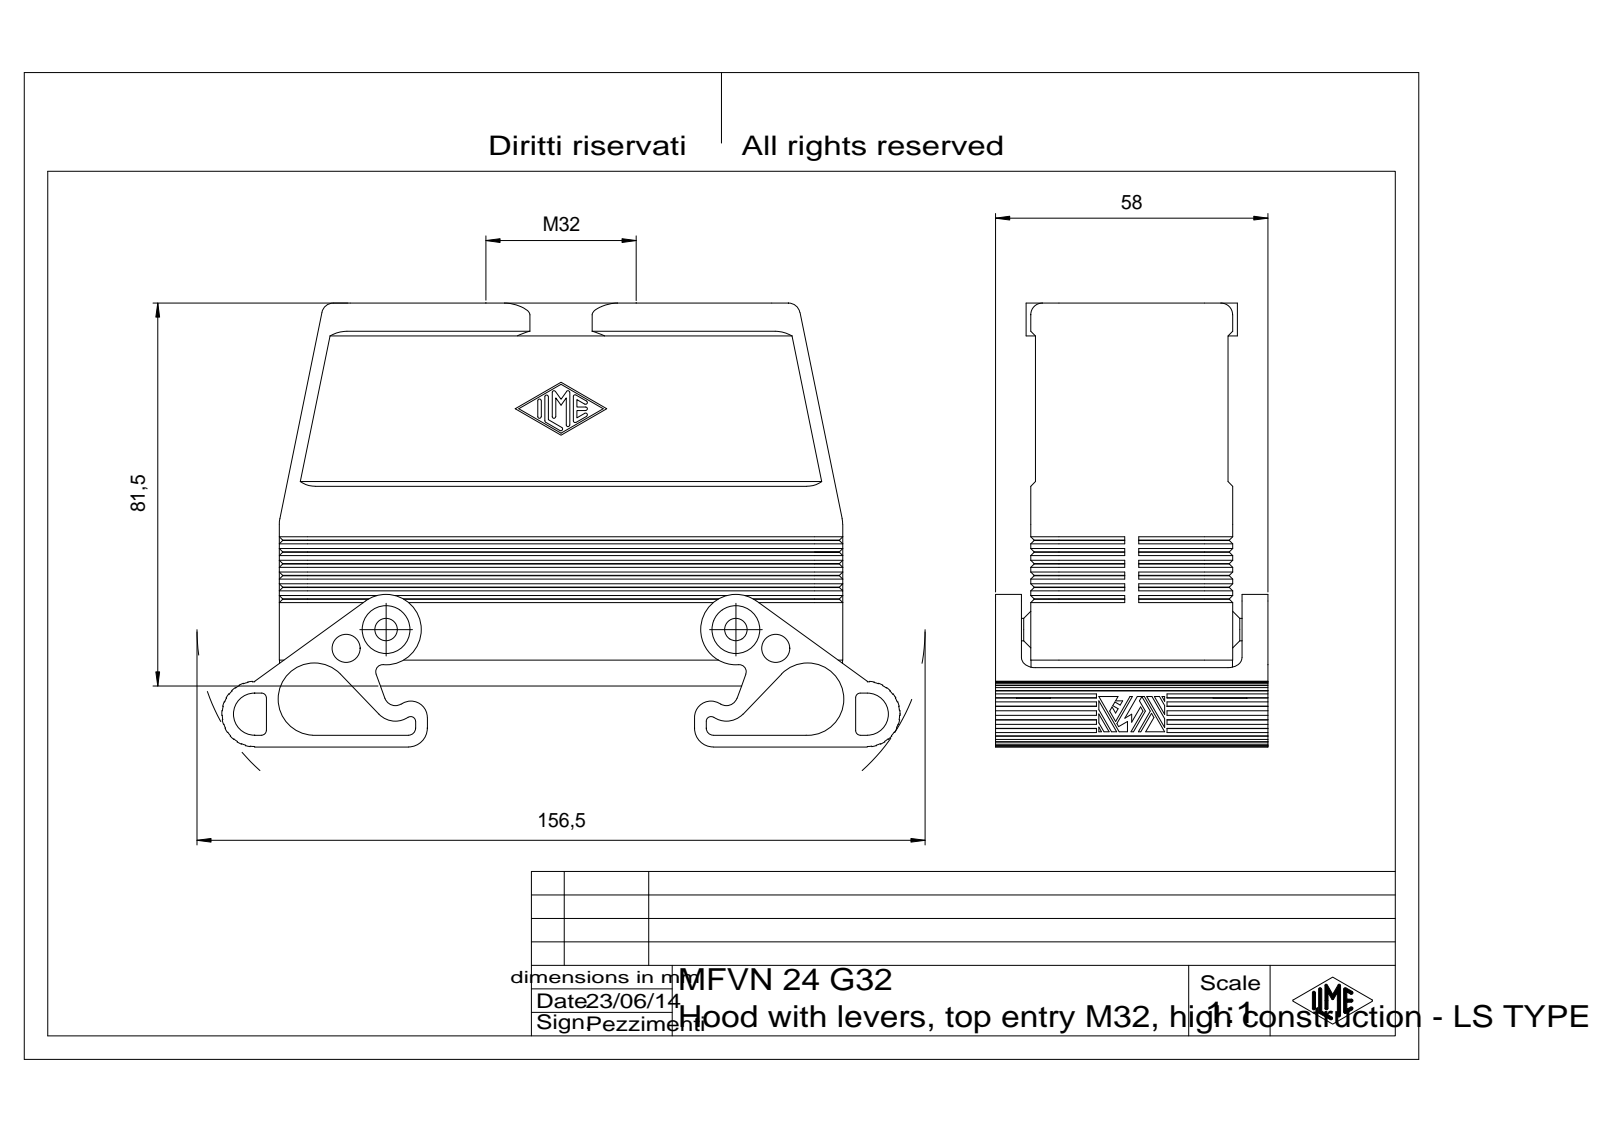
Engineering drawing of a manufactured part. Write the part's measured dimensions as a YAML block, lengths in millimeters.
part_name: "MFVN_24_G32"
step_written_by: "CoCreate Modeling 16.00A 16-Aug-2008 (C) Parametric Technology GmbH (AUTOMOTIVE_DESIGN)"
units: millimeters
bodies: {solids: 1, faces: 1170, planar: 568, cylindrical: 442, other: 160}
overall_size: [145.1, 94.5, 58]
volume: 126992
surface_area: 73979
round_holes:
  - {diameter: 2.46, count: 4}
  - {diameter: 4, count: 4}
  - {diameter: 6, count: 2}
  - {diameter: 10.2, count: 2}
  - {diameter: 32, count: 1}
round_bosses_or_shafts:
  - {diameter: 4.8, count: 2}
partial_cylinders:
  - {radius: 0.8, count: 16}
  - {radius: 1, count: 14}
  - {radius: 6, count: 14}
  - {radius: 3, count: 12}
  - {radius: 0.9, count: 8}
  - {radius: 0.2, count: 4}
  - {radius: 0.5, count: 4}
  - {radius: 1.5, count: 4}
face_to_face_distances: [3, 4, 39, 35, 38, 1, 42, 41, 6, 44]
hole_center_spacings: [53.72, 9.39, 27, 83.1, 104, 107.45, 74.5, 91.5]
